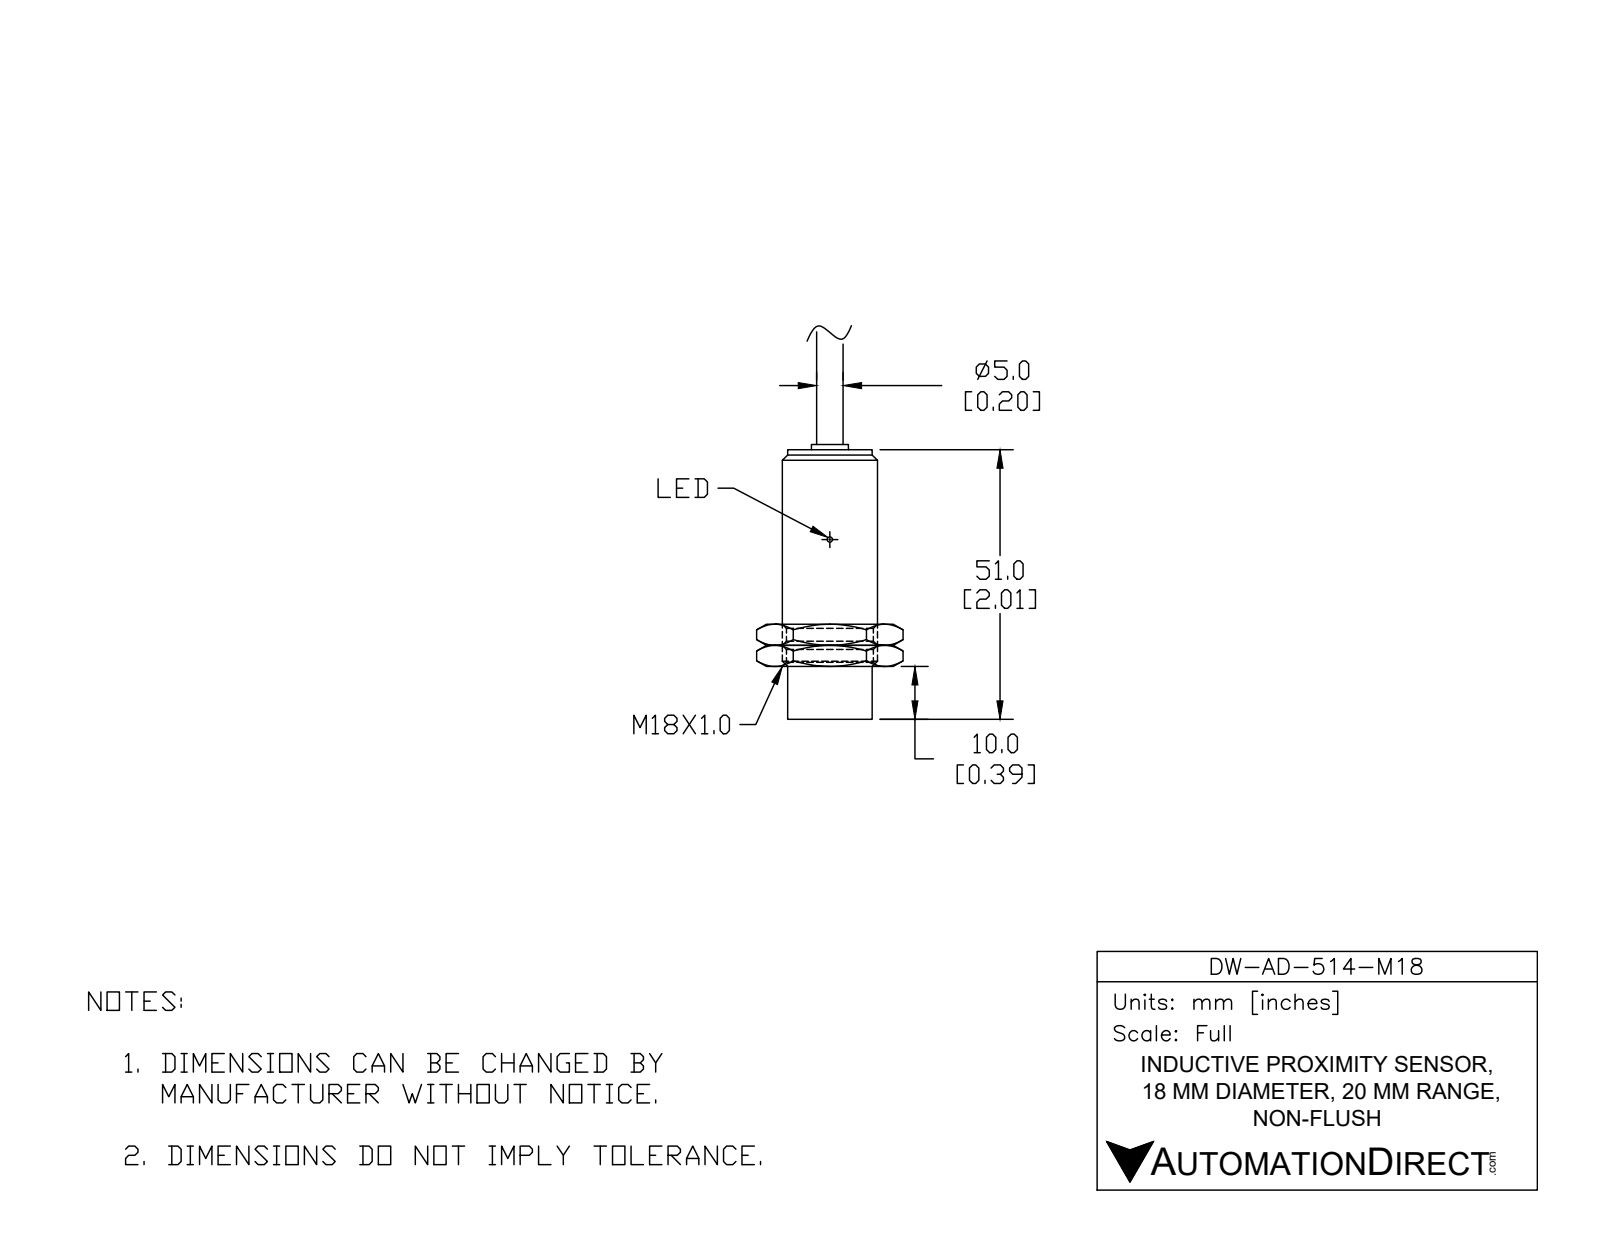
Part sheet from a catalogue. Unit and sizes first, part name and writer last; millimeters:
Units: millimetres
Overall size (bounding box): 76.6 × 18 × 18
Round bosses / shafts (diameter × count): ⌀18 ×1, ⌀16.5 ×1, ⌀16.4 ×1, ⌀10.5 ×1, ⌀6.8 ×1, ⌀5 ×1, ⌀3 ×1
Main face-to-face distances: 51, 0.8, 53, 2, 51.8, 1.2, 48, 3, 3.8, 5
Volume: 13 200 mm³ · Surface area: 3 815 mm²
Bodies: 2 solids, 37 faces (18 planar, 7 cylindrical, 12 other)
Part name (STEP PRODUCT): DW-AD-514-M18
STEP written by: SolidWorks 2017 (AUTOMOTIVE_DESIGN)
